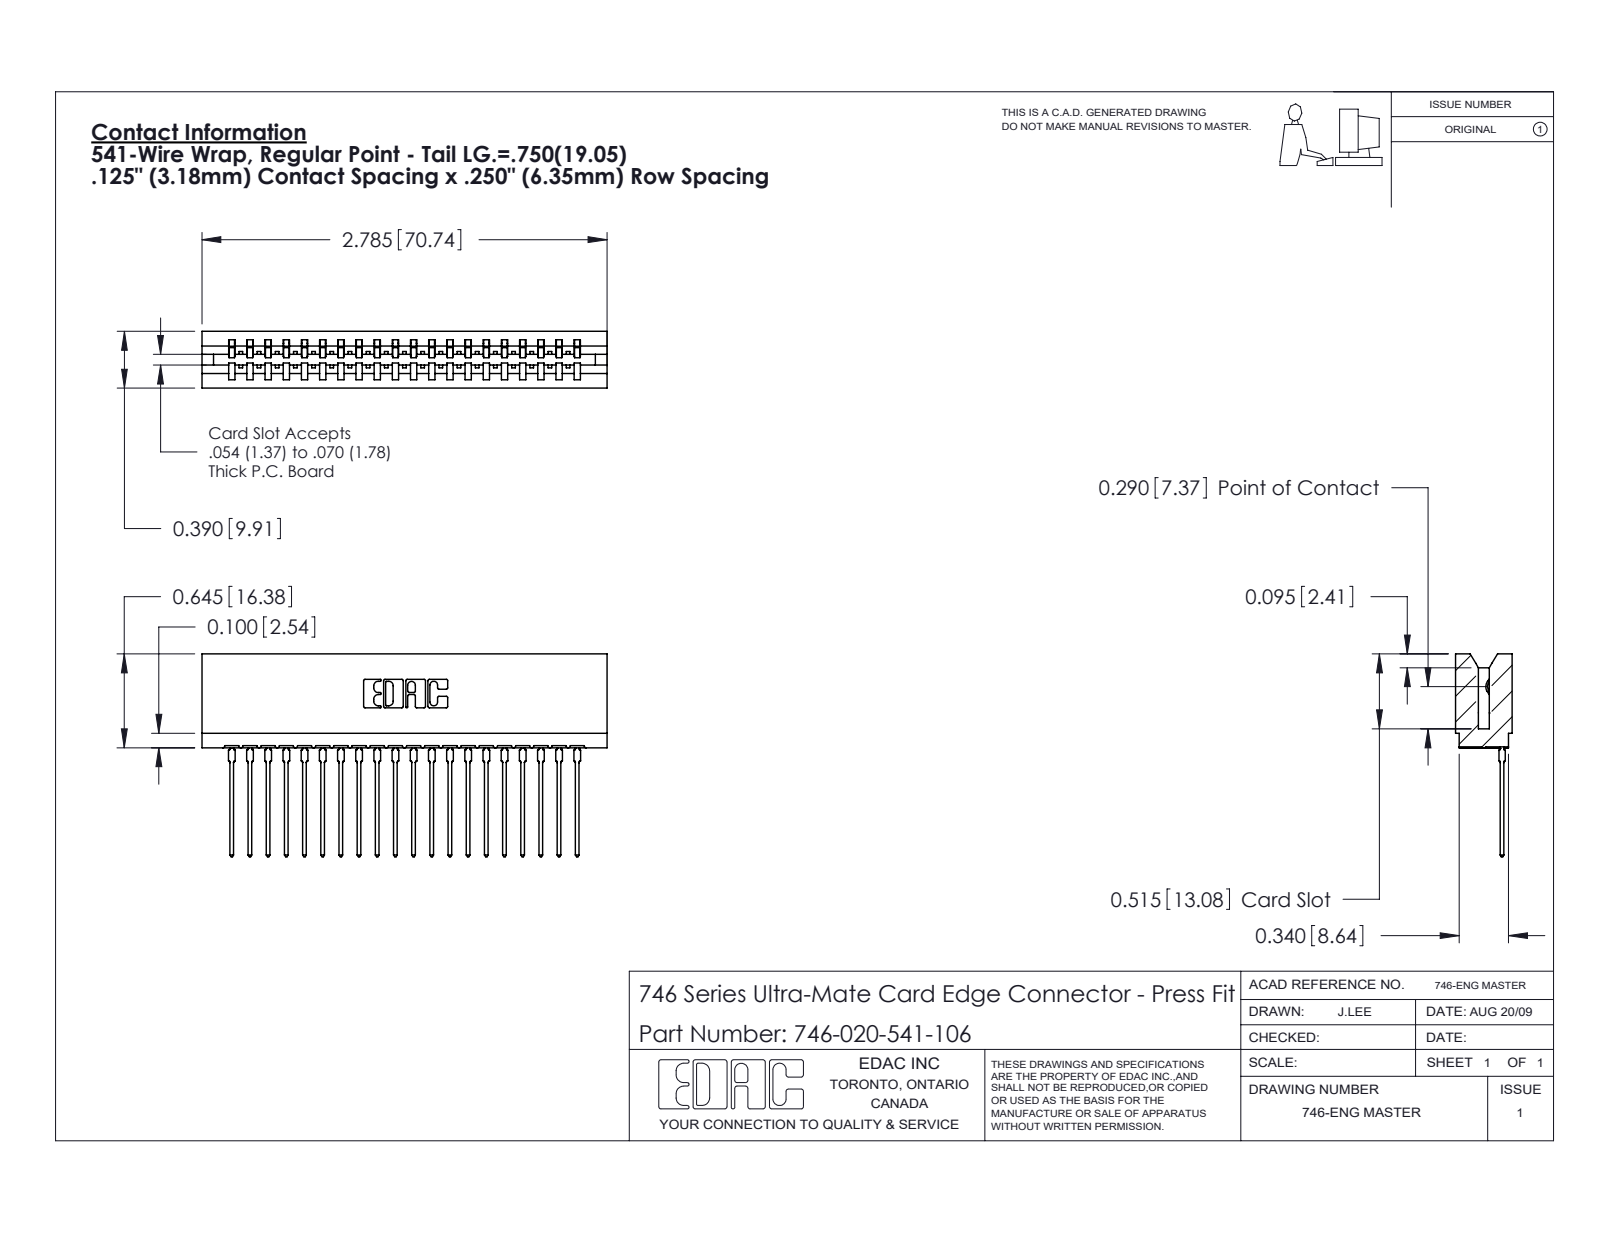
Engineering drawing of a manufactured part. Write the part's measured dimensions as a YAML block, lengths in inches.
part_name: "746-020-541-106; 746-292-001_541; 746 Part_.515 Slot Depth - 06"
step_written_by: "SolidWorks 2020 (CONFIG_CONTROL_DESIGN)"
units: inches
bodies: {solids: 21, faces: 2258, planar: 1316, cylindrical: 422, other: 520}
overall_size: [2.785, 1.394, 0.39]
volume: 0.465
surface_area: 17.69
partial_cylinders:
  - {radius: 0.021, count: 40}
  - {radius: 0.01, count: 22}
  - {radius: 0.015, count: 21}
  - {radius: 0.007, count: 6}
  - {radius: 0.031, count: 6}
  - {radius: 0.005, count: 4}
  - {radius: 0.011, count: 4}
  - {radius: 0.026, count: 3}
face_to_face_distances: [0.25, 0.333, 0.057, 0.39, 0.5, 0.025, 0.307, 0.083, 0.125, 0.375]
